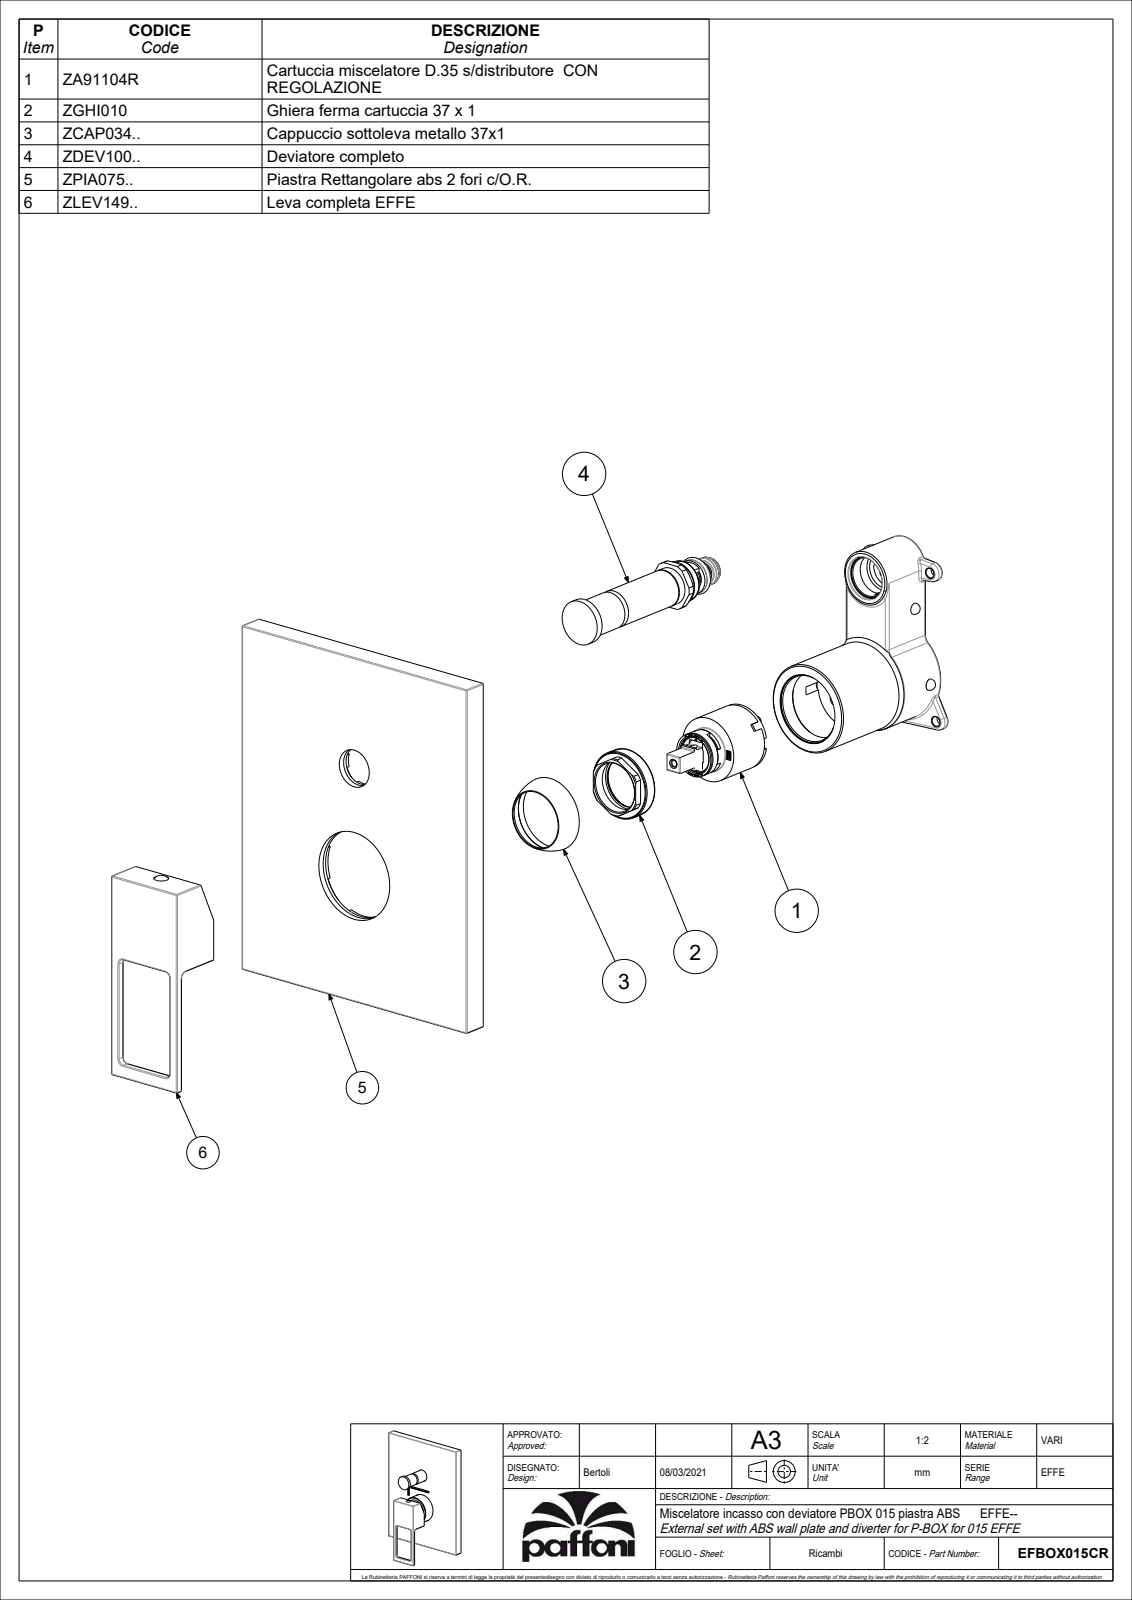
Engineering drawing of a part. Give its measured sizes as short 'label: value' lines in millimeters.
name: EFBOX015CR
written by: CREO PARAMETRIC BY PTC INC, 2020044 (CONFIG_CONTROL_DESIGN)
unit: mm
bodies: 5 solids, 1096 faces (658 planar, 287 cylindrical, 151 other)
size: 210.25 × 154 × 64.9
volume: 321 945 mm³; area: 128 770 mm²
holes: 3× ⌀5, 3× ⌀7, 2× ⌀2, 2× ⌀4, 1× ⌀3, 1× ⌀4.5, 1× ⌀5.5, 1× ⌀7.1, 1× ⌀7.8, 1× ⌀16, 1× ⌀18.2, 1× ⌀19.5
bosses: 2× ⌀4.8, 1× ⌀57, 1× ⌀48.1, 1× ⌀39, 1× ⌀35, 1× ⌀34.8, 1× ⌀32.2, 1× ⌀29
rounds: 51× R0.5, 11× R0.15, 5× R3, 4× R0.3, 2× R1, 1× R2.5, 1× R4, 1× R6.5
face distances: 13.5, 10, 3.5, 23.5, 31, 130.5, 54.5, 99.5, 76, 64.9
hole spacings: 8.6, 13.45, 15.13, 21.93, 50.8, 65.38, 9.5, 14
